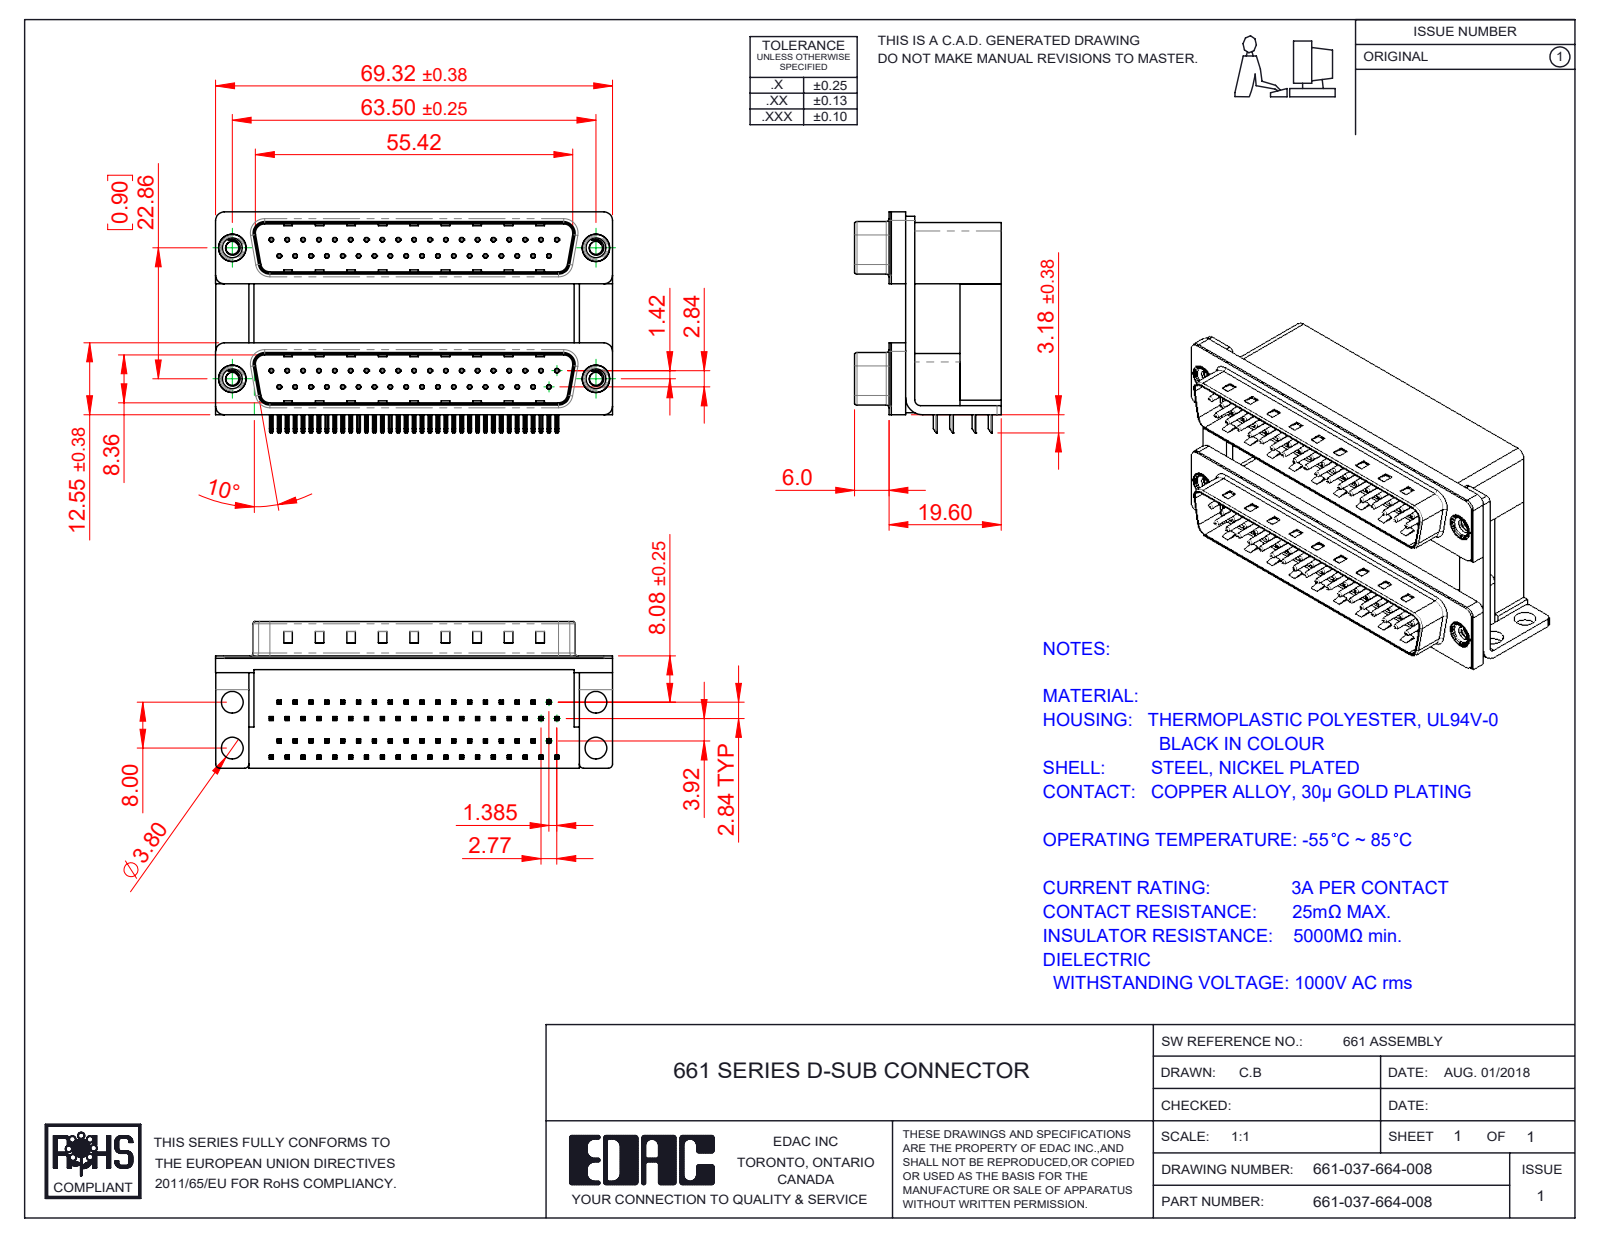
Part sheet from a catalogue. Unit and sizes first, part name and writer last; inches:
Units: inches
Overall size (bounding box): 2.729 × 1.519 × 1.008
Round holes (diameter × count): ⌀0.014 ×74, ⌀0.031 ×74, ⌀0.089 ×4, ⌀0.138 ×4, ⌀0.15 ×4, ⌀0.157 ×4, ⌀0.189 ×4, ⌀0.197 ×4
Round bosses / shafts (diameter × count): ⌀0.03 ×74, ⌀0.193 ×4, ⌀0.187 ×4, ⌀0.154 ×4
Partial cylindrical surfaces — rounded edges, fillets, slot ends (radius × count): R0.01 ×296, R0.005 ×148, R0.02 ×16, R0.059 ×14, R0.03 ×8, R0.035 ×8, R0.063 ×8, R0.079 ×8
Main face-to-face distances: 0.472, 0.9, 0.756, 0.016, 0.283, 0.421, 0.488, 0.112, 0.345, 0.886
Hole centre spacings: 0.109, 0.218, 0.124, 0.327, 0.436, 0.545, 0.654, 0.763
Volume: 1.88 in³ · Surface area: 48.28 in²
Bodies: 85 solids, 6582 faces (4250 planar, 1794 cylindrical, 538 other)
Part name (STEP PRODUCT): 661-037-664-008; 661 Housing Spacer_37 Contacts H; 661 Shell_37 Contacts; 661 Housing Lower_37 Contacts (+7 more)
STEP written by: SolidWorks 2020 (CONFIG_CONTROL_DESIGN)
